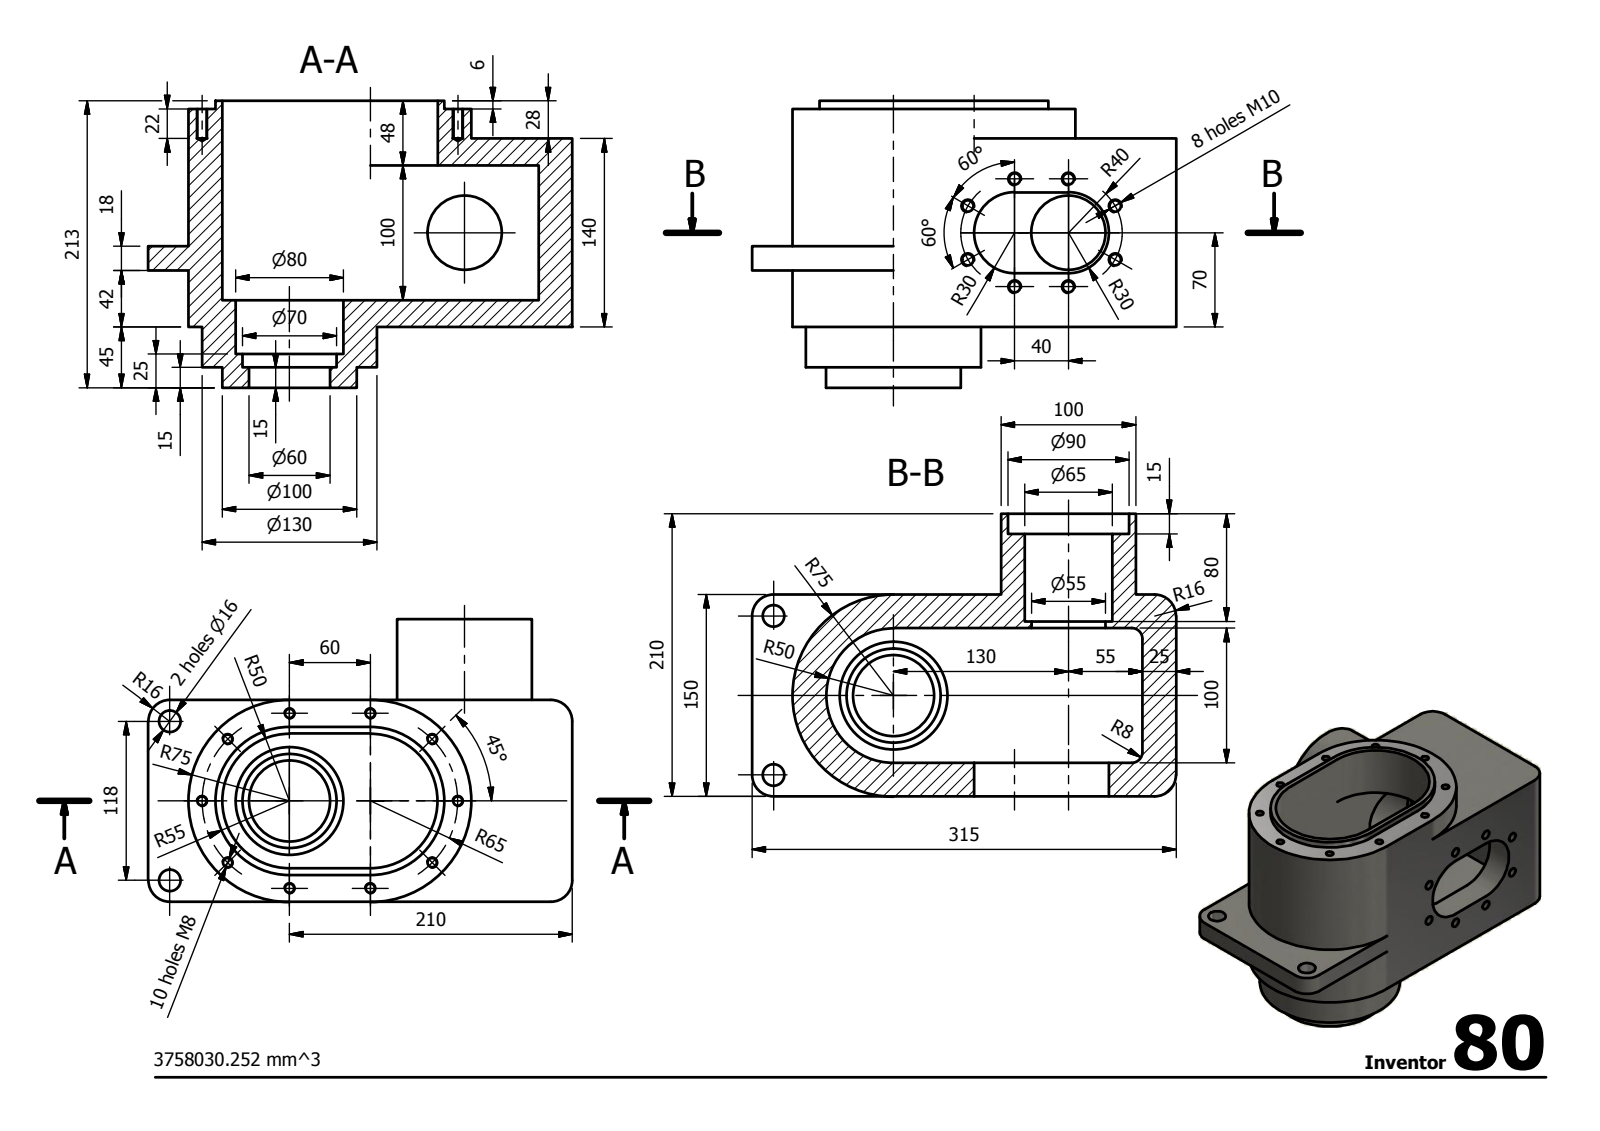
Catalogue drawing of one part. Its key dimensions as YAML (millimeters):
step_written_by: "Autodesk Inventor 2014 (AUTOMOTIVE_DESIGN)"
units: millimeters
bodies: {solids: 1, faces: 80, planar: 26, cylindrical: 44, other: 10}
overall_size: [315, 213, 210]
volume: 3758000
surface_area: 387830
round_holes:
  - {diameter: 6.65, count: 10}
  - {diameter: 8.38, count: 8}
  - {diameter: 16, count: 2}
  - {diameter: 55, count: 1}
  - {diameter: 60, count: 1}
  - {diameter: 65, count: 1}
  - {diameter: 70, count: 1}
  - {diameter: 80, count: 1}
  - {diameter: 90, count: 1}
  - {diameter: 100, count: 1}
round_bosses_or_shafts:
  - {diameter: 130, count: 1}
  - {diameter: 100, count: 1}
partial_cylinders:
  - {radius: 16, count: 4}
  - {radius: 8, count: 2}
  - {radius: 30, count: 2}
  - {radius: 55, count: 2}
  - {radius: 75, count: 2}
  - {radius: 50, count: 1}
face_to_face_distances: [25, 125, 20, 120, 150, 100, 22, 60, 42, 140]
hole_center_spacings: [40, 49.75, 77.27, 91.92, 65, 69.28, 95.77, 107.66]
